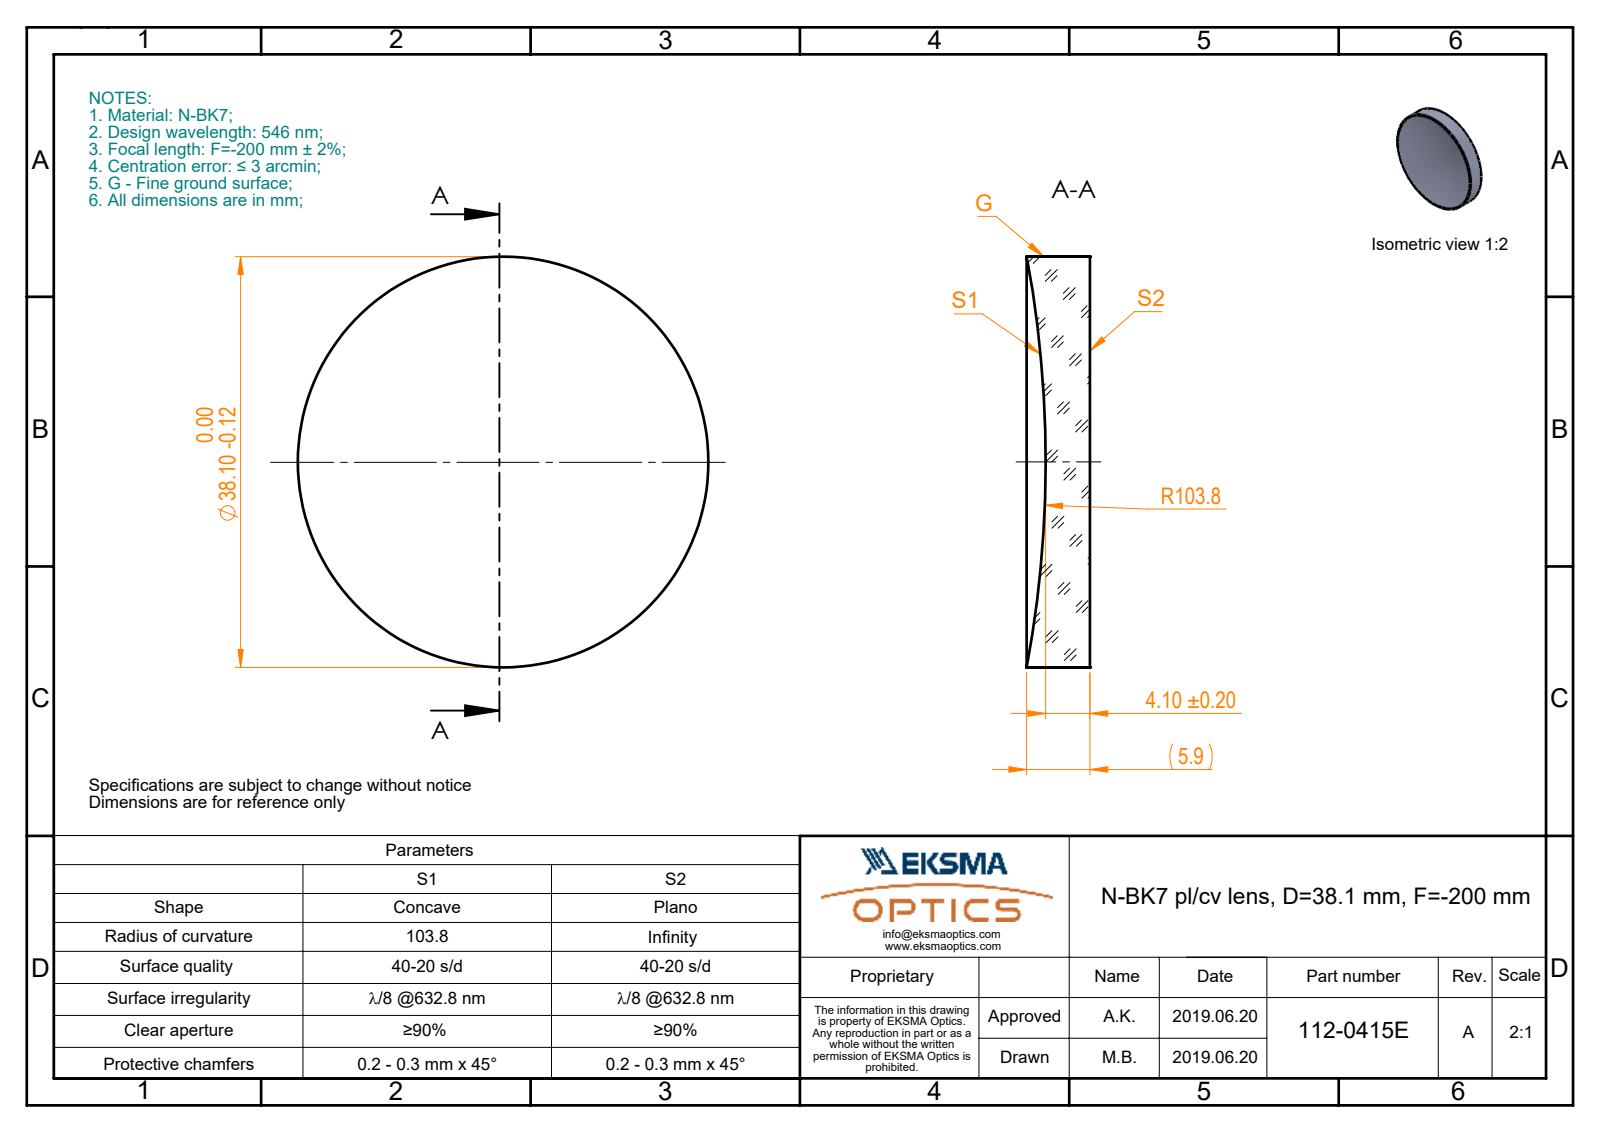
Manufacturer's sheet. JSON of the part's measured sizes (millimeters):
{"part_name": "112-0415E BK7 pl-cv 38.1 F-200", "step_written_by": "SolidWorks 2017 (CONFIG_CONTROL_DESIGN)", "units": "millimeters", "bodies": {"solids": 1, "faces": 5, "planar": 1, "cylindrical": 2, "other": 2}, "overall_size": [38.1, 38.1, 5.87], "volume_mm3": 5678, "surface_area_mm2": 2992, "round_bosses_or_shafts": [[38.1, 1]]}
